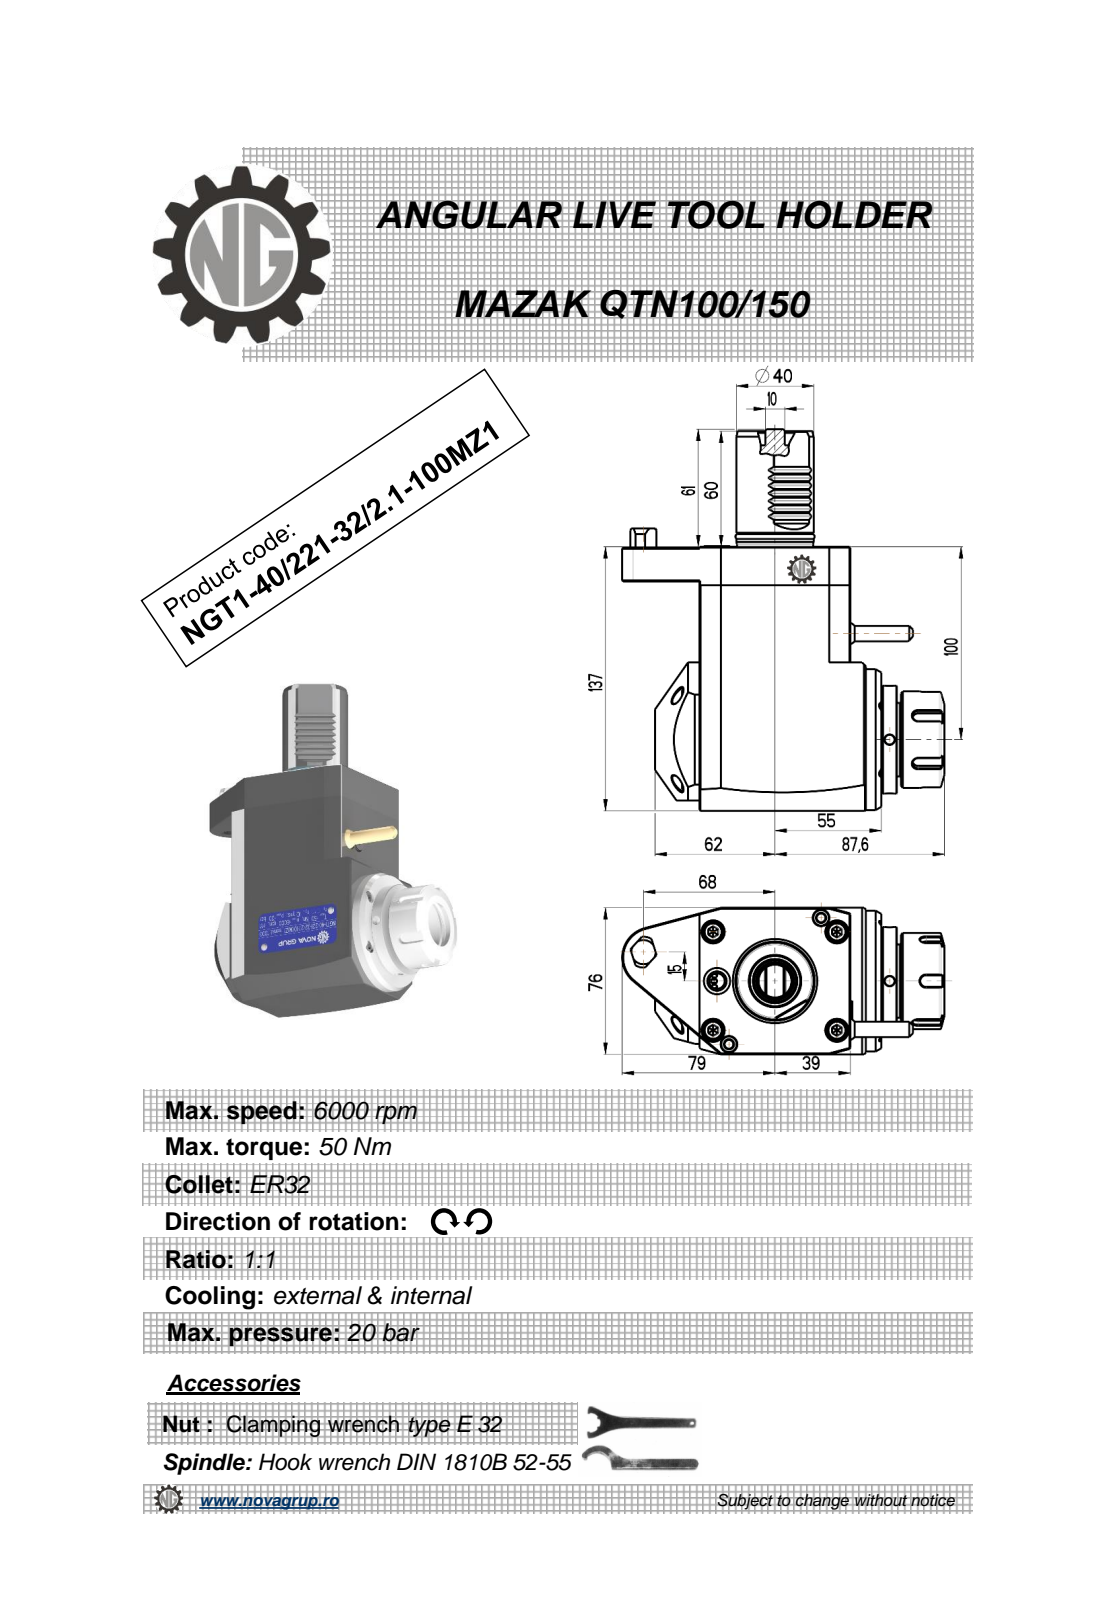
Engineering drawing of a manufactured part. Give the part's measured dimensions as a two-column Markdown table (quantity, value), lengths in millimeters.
| quantity | value |
| --- | --- |
| part name | NGT1_40_221_32_2_1_100MZ1 |
| STEP written by | PRO/ENGINEER BY PARAMETRIC TECHNOLOGY CORPORATION, 2010280 (CONFIG_CONTROL_DESIGN) |
| units | millimeters |
| bodies | 1 solid, 300 faces (133 planar, 76 cylindrical, 91 other) |
| overall size | 198 × 166.6 × 76 |
| volume | 1 102 000 mm³ |
| surface area | 82 494 mm² |
| round holes (diameter × count) | 5 × 3, 3 × 1, 8 × 1, 26 × 1, 27 × 1 |
| round bosses / shafts (diameter × count) | 73 × 1, 56 × 1, 50 × 1, 43 × 1, 40 × 1, 39.4 × 1, 36.2 × 1, 10 × 1 |
| partial cylindrical surfaces (radius × count) | 0.3 × 7, 0.2 × 6, 3 × 5, 0.8 × 2, 300 × 2, 8 × 1, 9 × 1, 15.84 × 1 |
| main face-to-face distances | 76, 78, 137, 8, 16, 94, 18, 119, 87.92, 7.5 |
| hole center spacings | 30, 59.25, 60.42, 89.25 |
